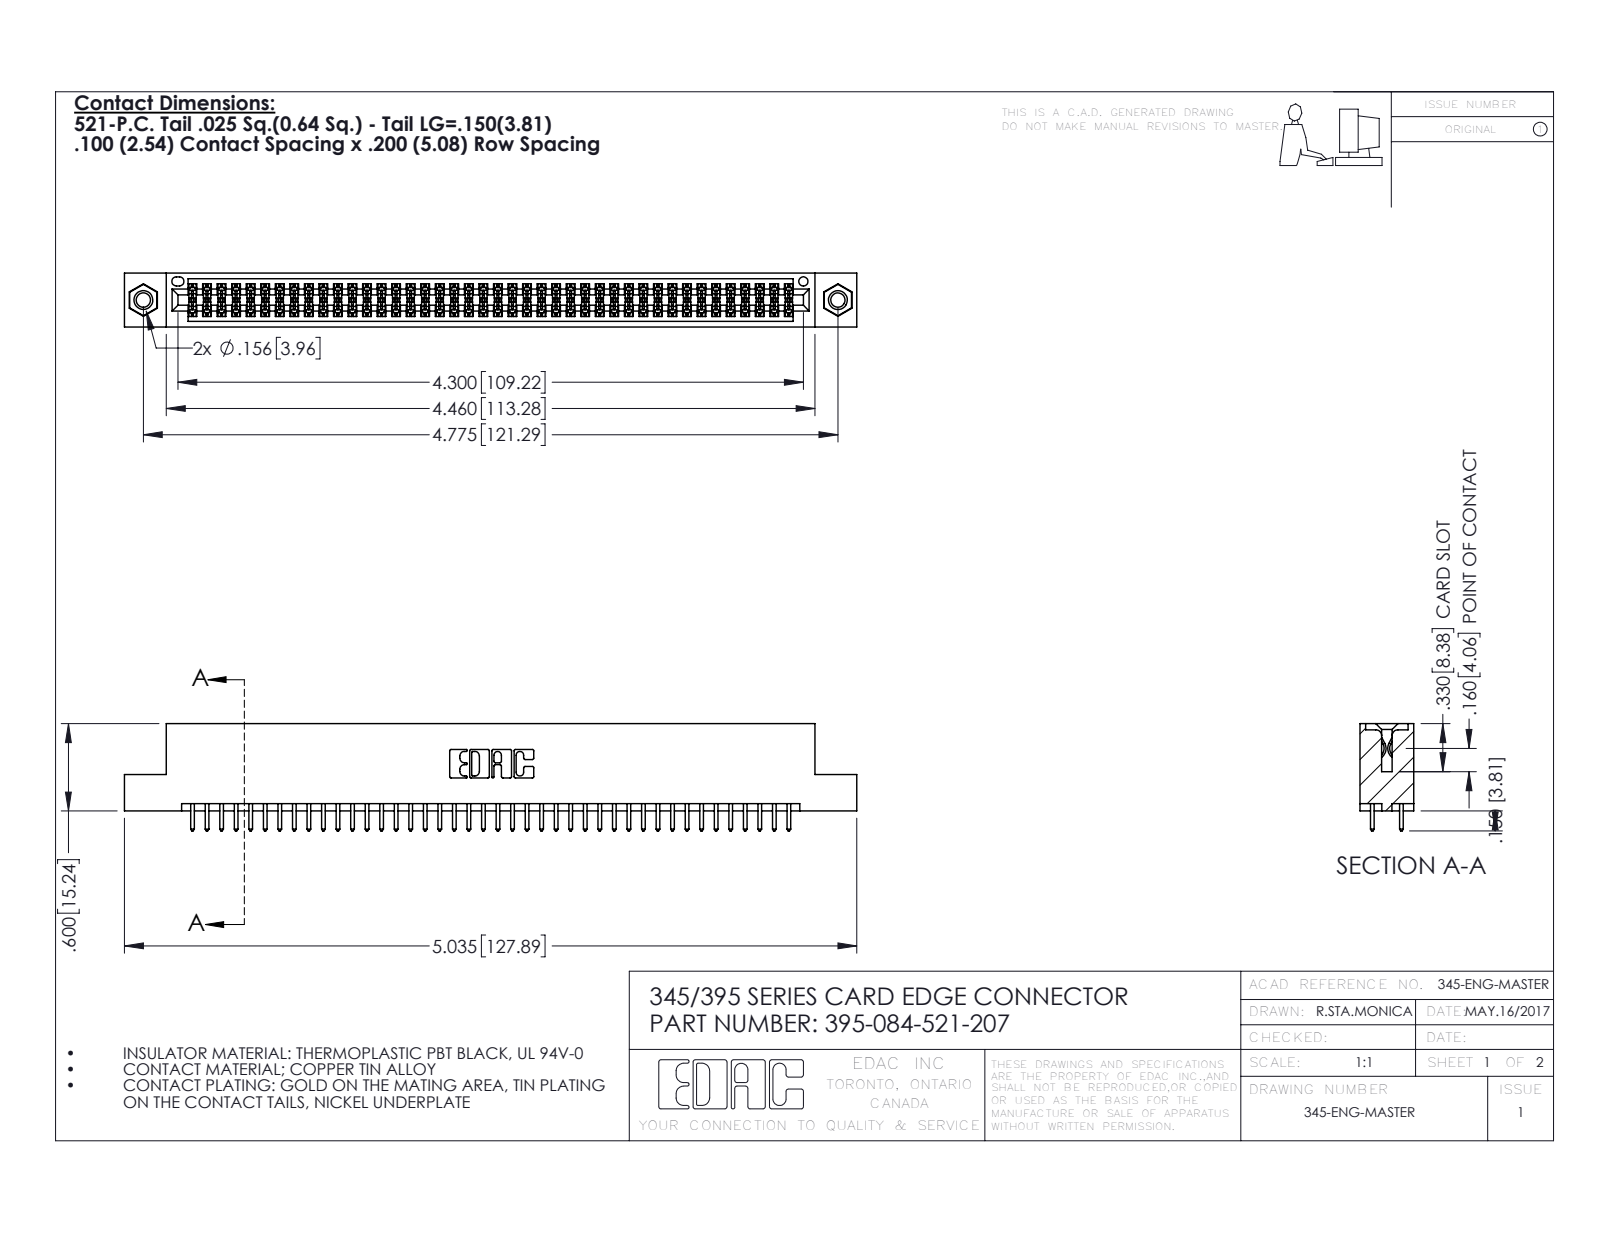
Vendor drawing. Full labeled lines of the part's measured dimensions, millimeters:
Part name (STEP PRODUCT): 345-292-001_345-293-121; 345-250-001_345-250-005-103; 345 Part_Flush Mounting Lugs - 0.156 Dia-TI; 395-084-521-207
STEP written by: SolidWorks 2016 (CONFIG_CONTROL_DESIGN)
Units: millimetres
Bodies: 87 solids, 4386 faces (2884 planar, 1486 cylindrical, 16 other)
Overall size (bounding box): 127.9 × 18.7 × 9.4
Volume: 12 400 mm³ · Surface area: 18 100 mm²
Round holes (diameter × count): ⌀2.5 ×2, ⌀3.2 ×2, ⌀4 ×2, ⌀1.6 ×1
Round bosses / shafts (diameter × count): ⌀3.9 ×2
Partial cylindrical surfaces — rounded edges, fillets, slot ends (radius × count): R0.2 ×126, R0.3 ×84, R0.3 ×22, R0.2 ×6, R0.8 ×6, R0.7 ×3, R0.4 ×2, R0.5 ×2
Main face-to-face distances: 1.8, 7.6, 5.1, 9.4, 2.5, 6.9, 0.6, 5.7, 4.4, 3.8
Hole centre spacings: 6.9, 115.3, 121.3
